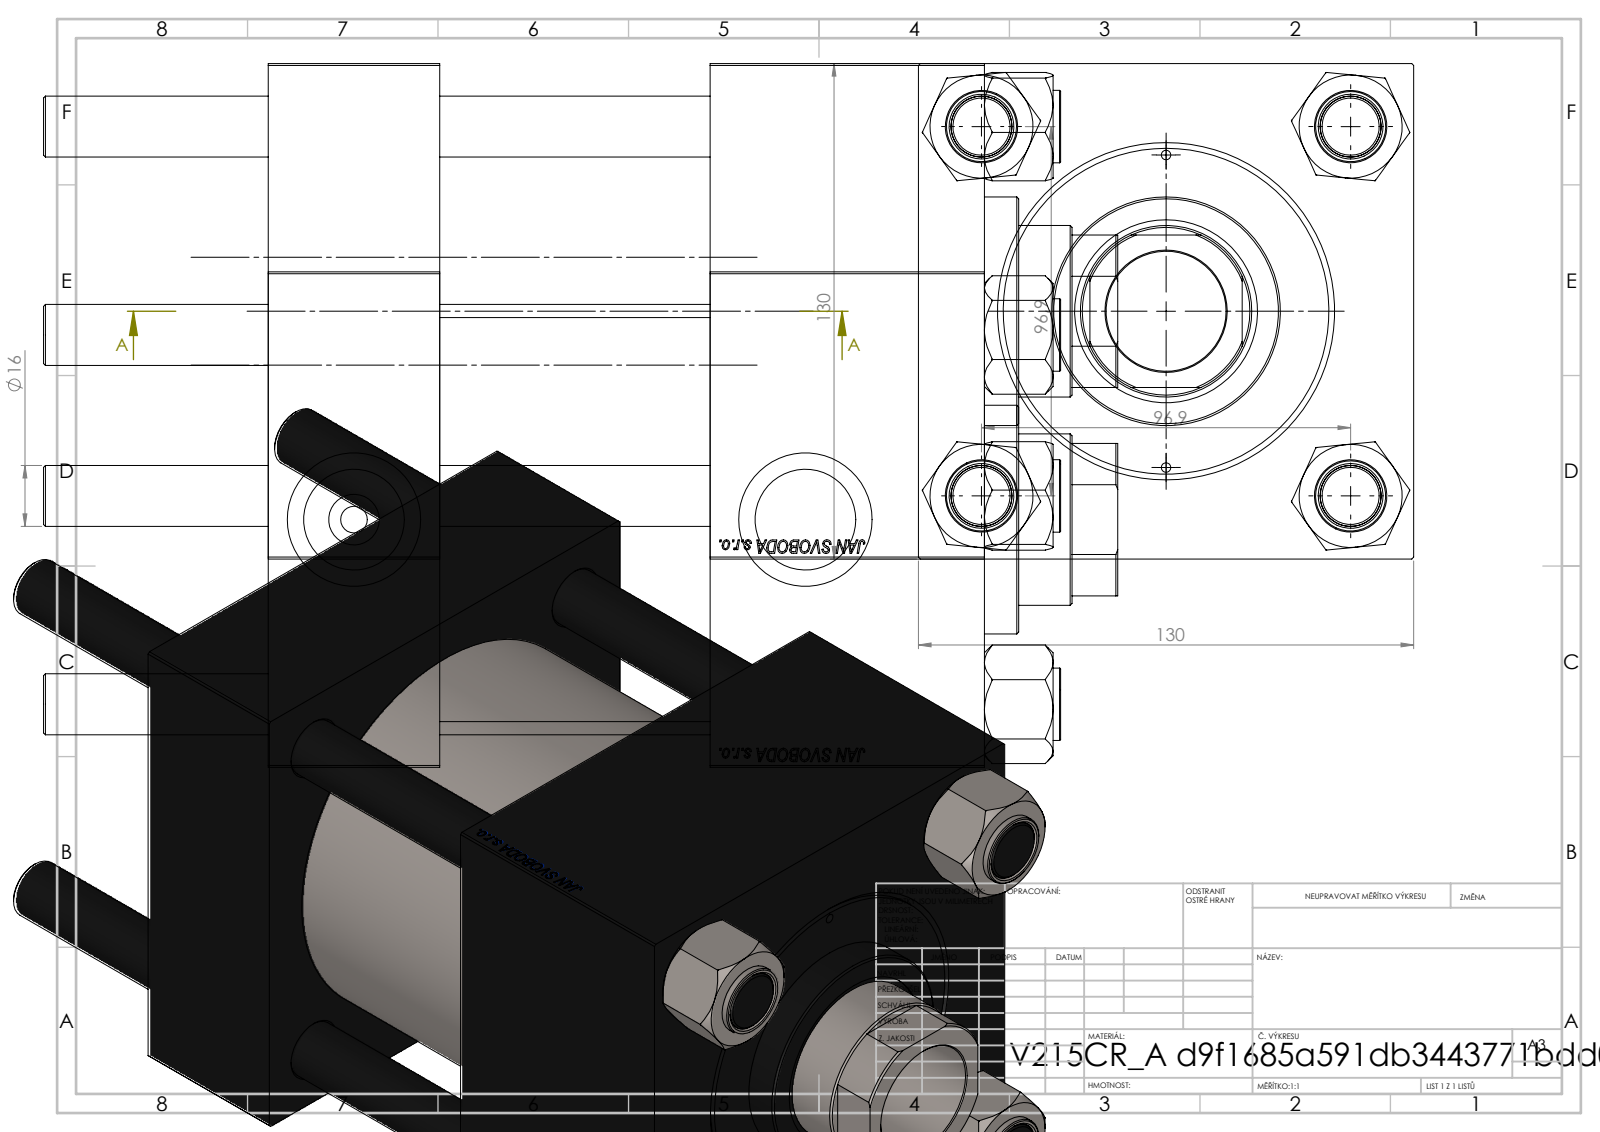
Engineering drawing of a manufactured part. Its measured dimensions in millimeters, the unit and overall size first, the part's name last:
Units: millimetres
Overall size (bounding box): 282 × 130 × 130
Round holes (diameter × count): ⌀16 ×4, ⌀2.5 ×2, ⌀7 ×2, ⌀26.44 ×2, ⌀35 ×2, ⌀31.5 ×1, ⌀45 ×1, ⌀48 ×1, ⌀76 ×1, ⌀85.5 ×1, ⌀100 ×1
Round bosses / shafts (diameter × count): ⌀19 ×4, ⌀106 ×1, ⌀60 ×1
Partial cylindrical surfaces — rounded edges, fillets, slot ends (radius × count): R22 ×1
Main face-to-face distances: 130, 45, 188, 143, 116, 71, 72, 20, 92, 96
Hole centre spacings: 49.02, 68.52, 96.9, 101.73, 41, 137.04, 82, 118.5
Volume: 2 504 000 mm³ · Surface area: 353 689 mm²
Bodies: 11 solids, 1188 faces (570 planar, 82 cylindrical, 536 other)
Part name (STEP PRODUCT): NUT_M5; CR025_012_A_0_G_A_G_M_020_+#_##_TYCINKA; V215CR_BODY_A; V215_VC_A (+1 more)
STEP written by: SolidWorks 2019 (CONFIG_CONTROL_DESIGN)
